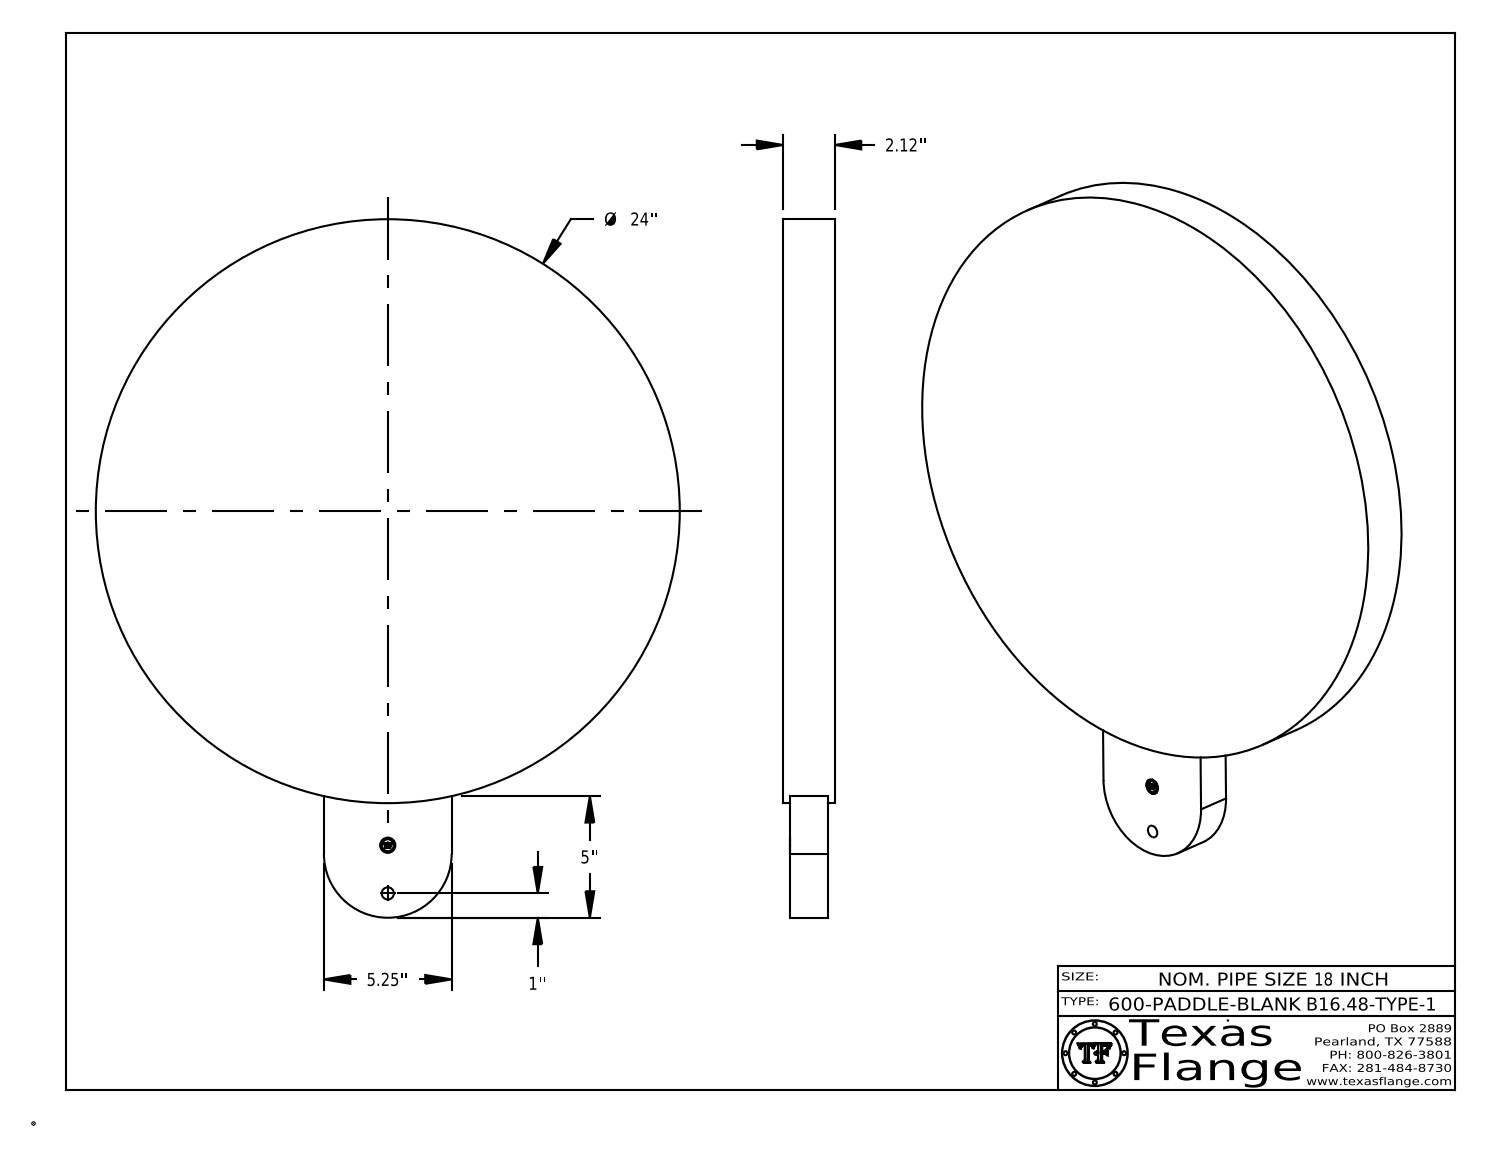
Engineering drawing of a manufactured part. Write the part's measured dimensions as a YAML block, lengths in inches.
part_name: "18-600-PADDLE-BLANK-B16.48-TYPE-1"
step_written_by: "CATIA V5 STEP AP214 (AUTOMOTIVE_DESIGN)"
units: inches
bodies: {solids: 1, faces: 396, planar: 371, cylindrical: 25, other: 0}
overall_size: [28.709, 24, 2.12]
volume: 994.2
surface_area: 1124
round_holes:
  - {diameter: 0.5, count: 1}
  - {diameter: 0.625, count: 1}
round_bosses_or_shafts:
  - {diameter: 0.038, count: 8}
  - {diameter: 24, count: 1}
  - {diameter: 0.492, count: 1}
partial_cylinders:
  - {radius: 2.625, count: 1}
face_to_face_distances: [2.12, 0.265, 1.855, 1.59, 5.25, 1.84, 1.575, 0.015, 0.28, 2.563]
hole_center_spacings: [1.98]
